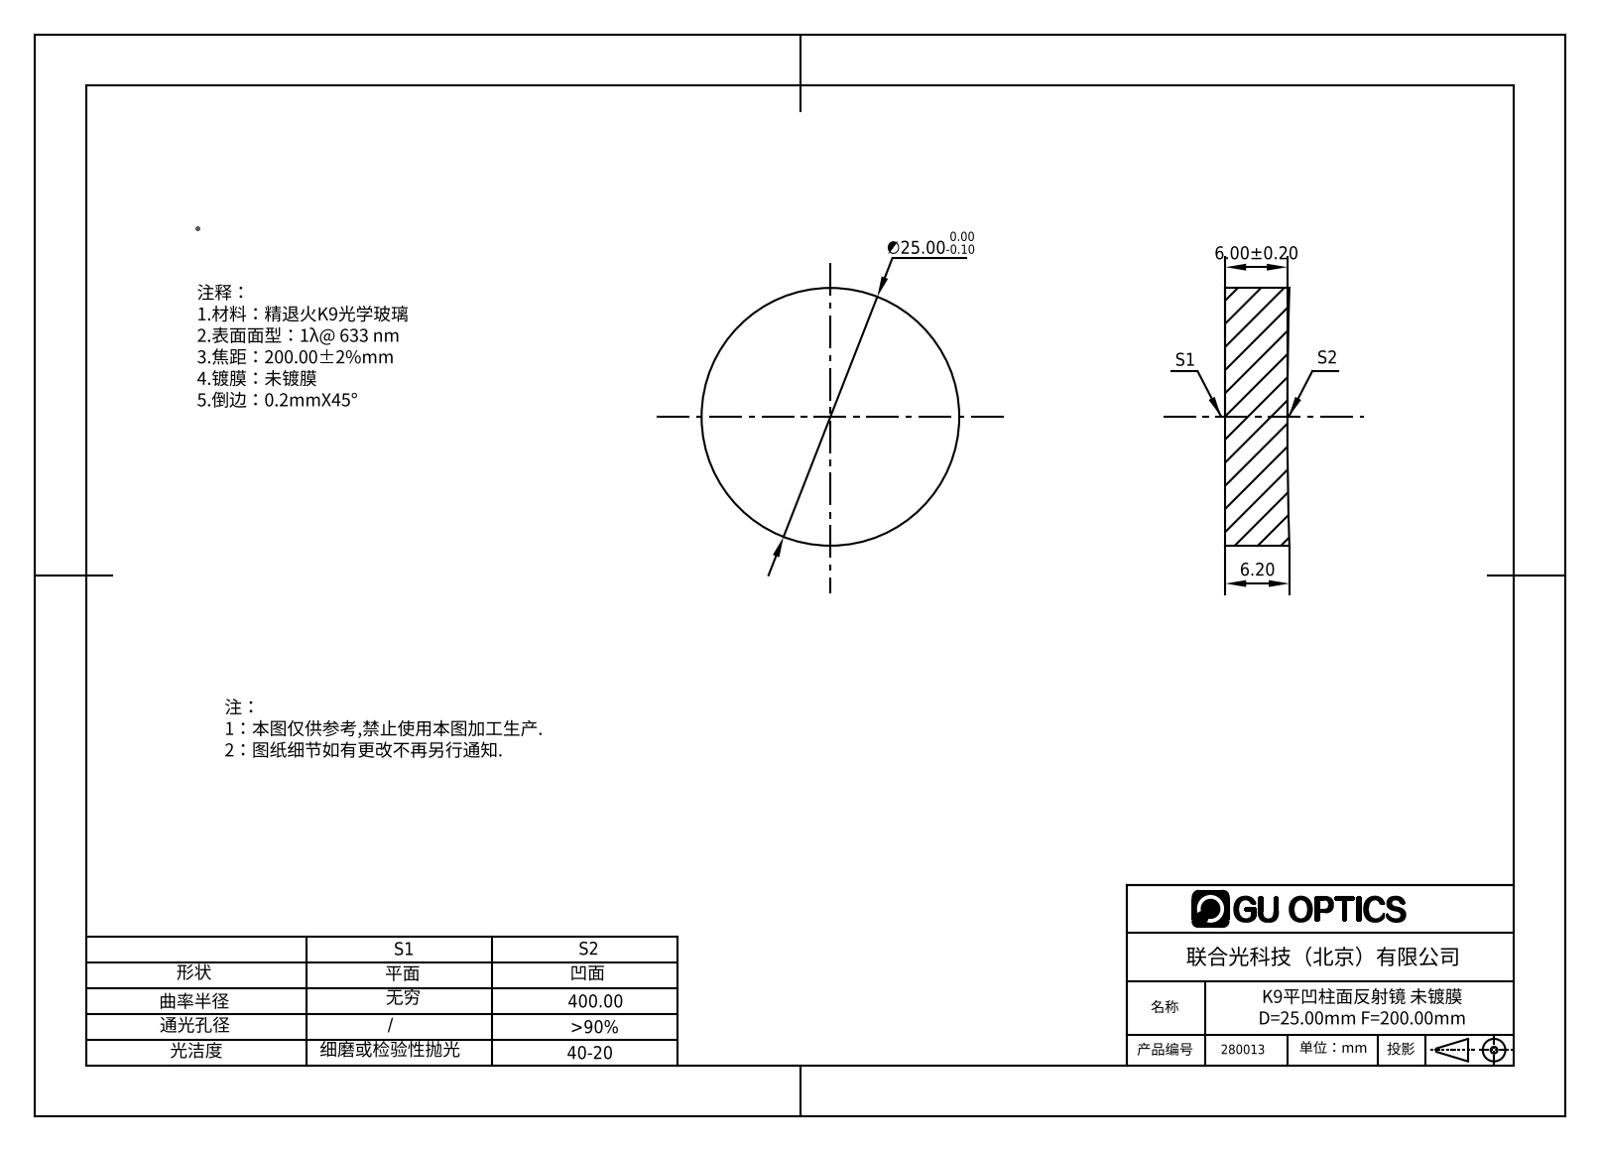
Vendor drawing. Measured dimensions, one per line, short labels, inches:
name: 280013
written by: SolidWorks 2020 (CONFIG_CONTROL_DESIGN)
unit: in
bodies: 1 solid, 3 faces (1 planar, 2 cylindrical, 0 other)
size: 0.984 × 0.984 × 0.244
volume: 0.181 in³; area: 2.265 in²
bosses: 1× ⌀0.984
rounds: 1× R15.748
